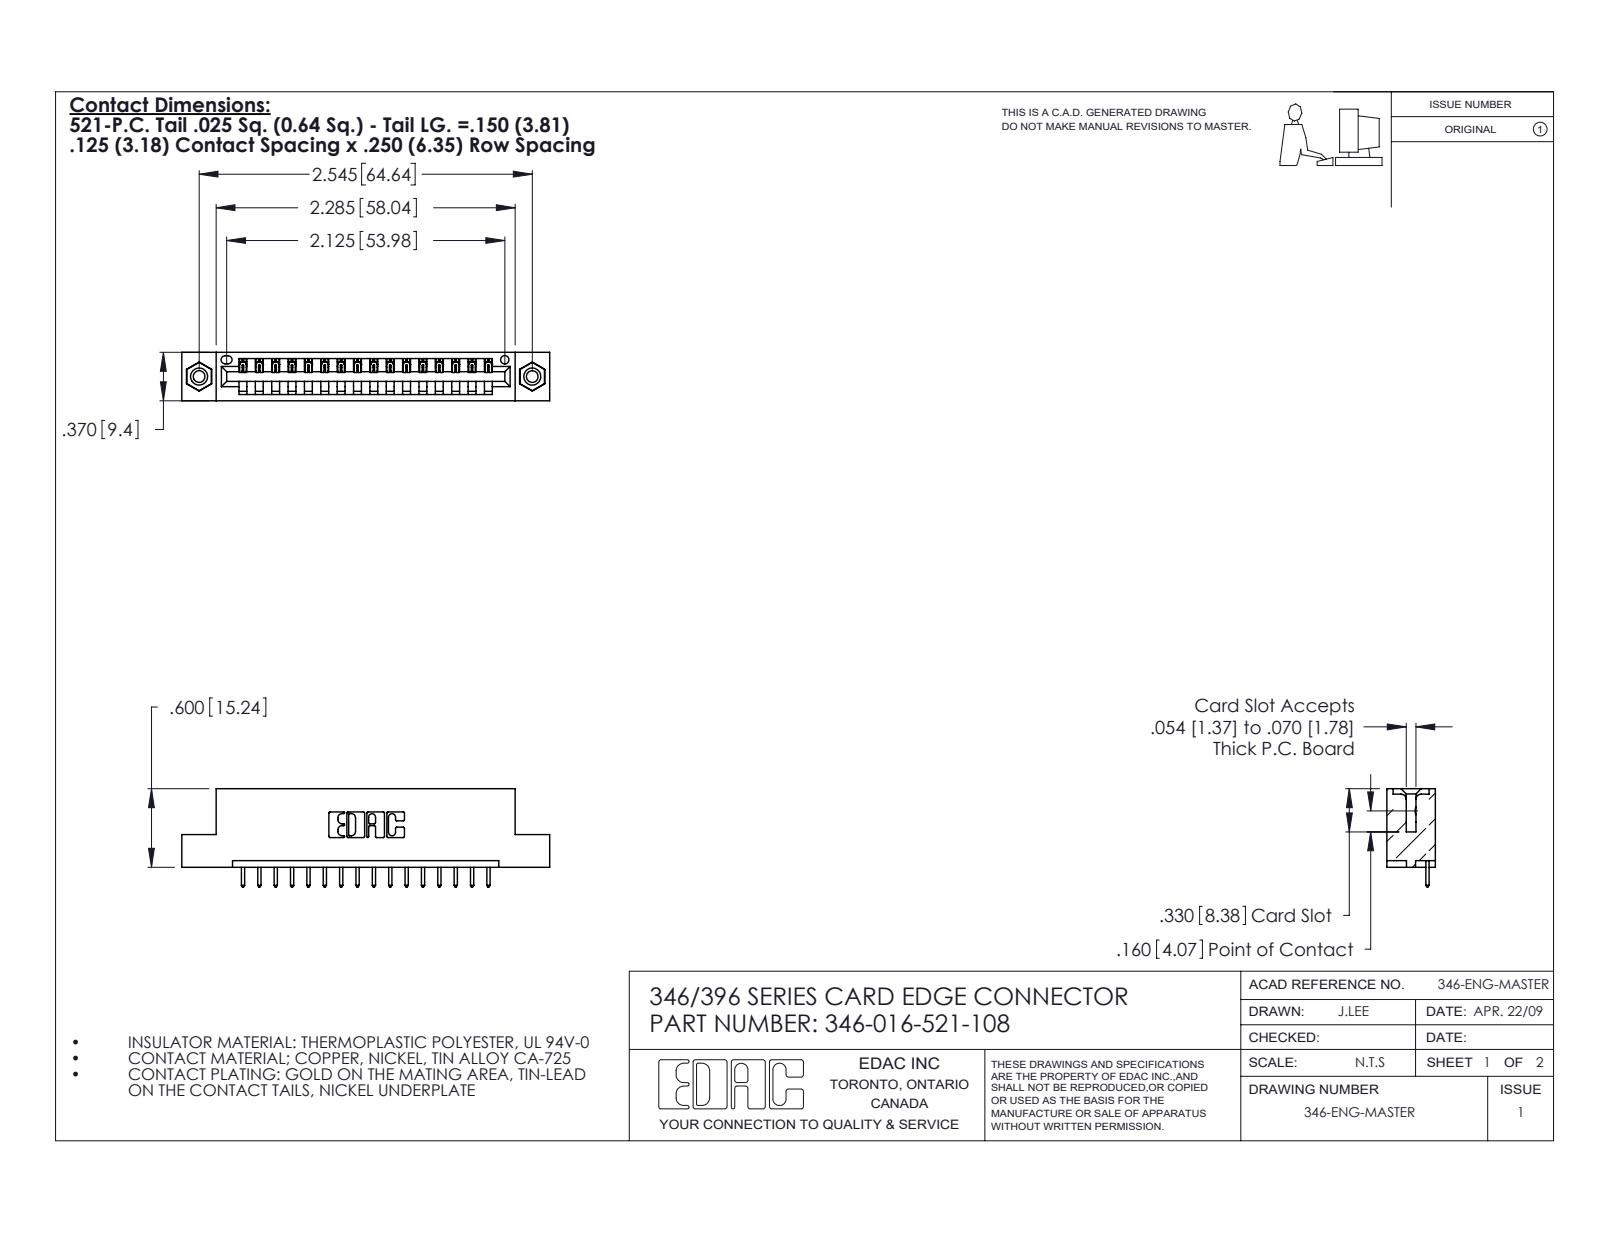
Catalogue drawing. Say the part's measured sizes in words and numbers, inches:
The part is named "345-250-001_345-250-003-102; 346-016-521-108; 345-292-001_345-293-121; 346 Part_Flush Mounting Lugs - 0.156 Dia-TI". Its 3-D file was written by "SolidWorks 2020 (CONFIG_CONTROL_DESIGN)". It is 19 solids with 1110 faces: 748 planar, 346 cylindrical and 16 other. Overall it measures 2.81 by 0.75 by 0.37 inches. Its volume is 0.403 cubic inches and its surface area 12.11 square inches. Round holes: 2 of diameter 0.089, 2 of diameter 0.125, 2 of diameter 0.156, 1 of diameter 0.064. Round bosses or shafts: 2 of diameter 0.155. Partial cylindrical surfaces (rounded edges, fillets, slot ends): 32 of radius 0.006, 32 of radius 0.01, 22 of radius 0.01, 6 of radius 0.007, 6 of radius 0.031, 3 of radius 0.026, 2 of radius 0.031, 2 of radius 0.04. The main face-to-face distances are 0.048, 0.322, 0.25, 0.37, 0.072, 0.298, 0.025, 0.148, 0.222, 0.1. The hole center spacings are 0.246, 2.338, 2.545.
